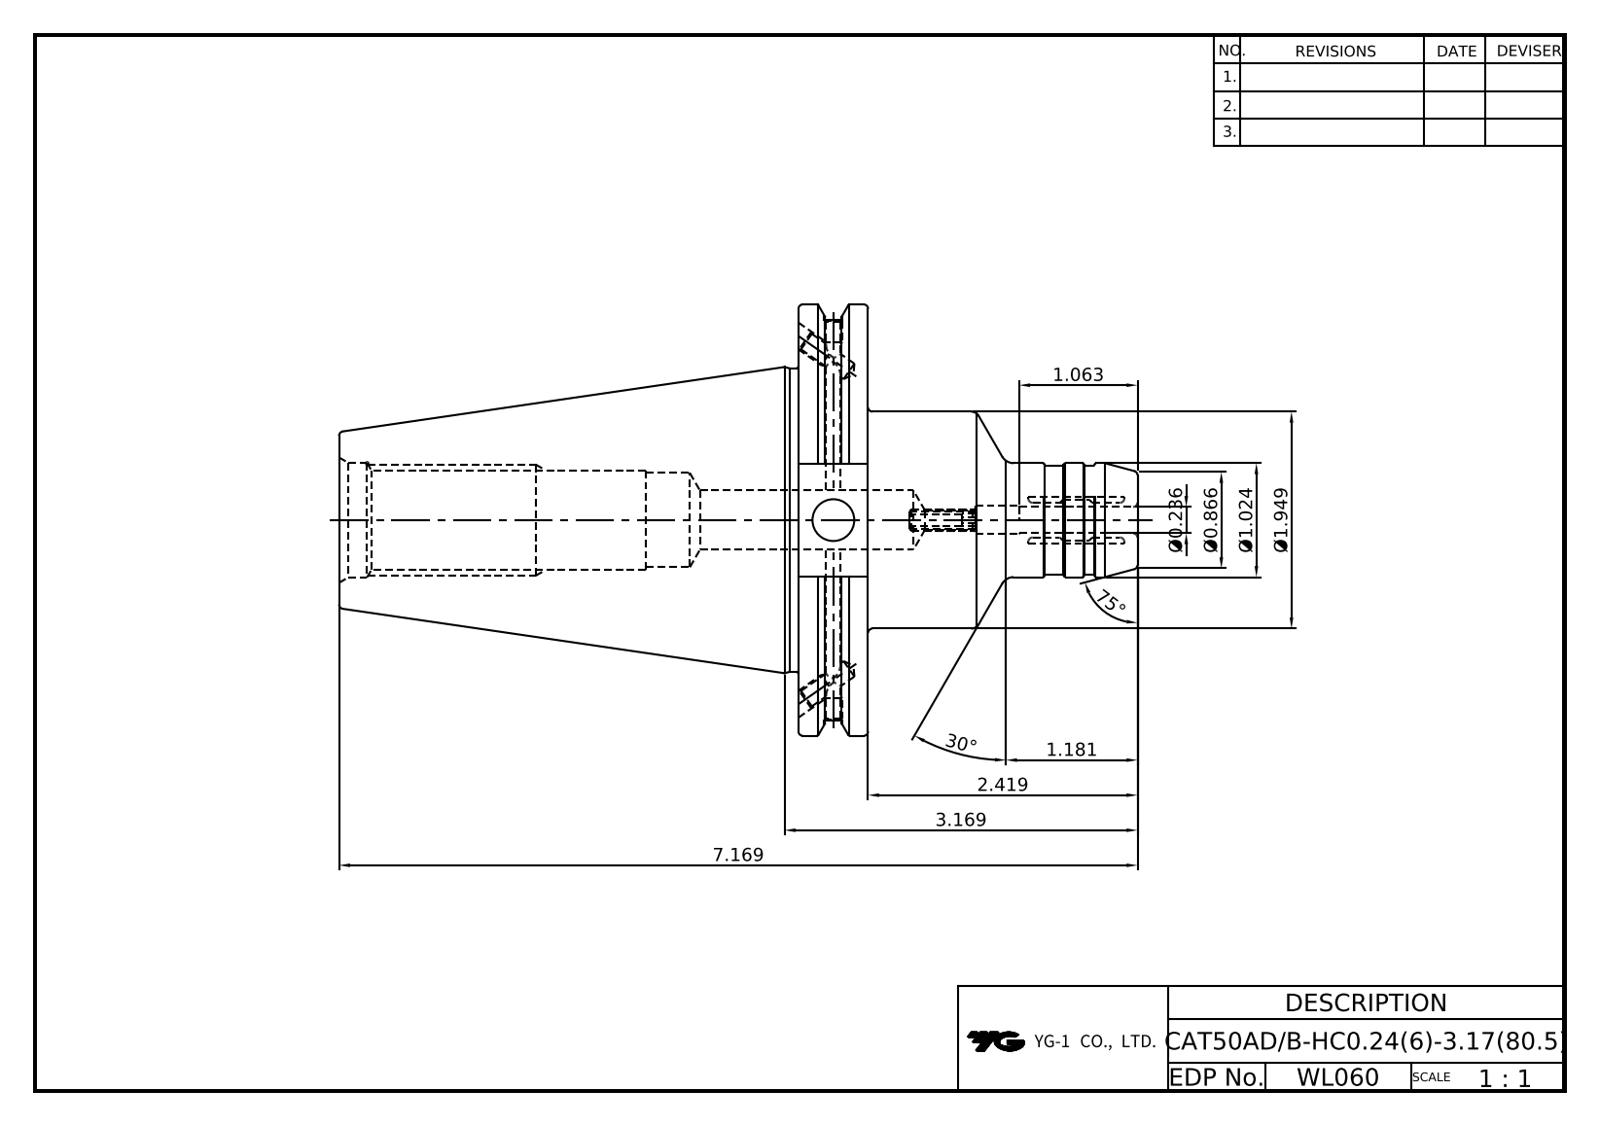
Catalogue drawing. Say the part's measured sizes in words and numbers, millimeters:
The part is named "LO-CAT50ADB-HC6-80.5". Its 3-D file was written by "Autodesk Inventor 2022 (AUTOMOTIVE_DESIGN)". It is 1 solid with 108 faces: 37 planar, 33 cylindrical and 38 other. Overall it measures 182.1 by 98.42 by 94.69 millimeters. Its volume is 395 201 cubic millimeters and its surface area 51 850 square millimeters. Round holes: 2 of diameter 3.24, 2 of diameter 4.13, 2 of diameter 4.2, 2 of diameter 5, 1 of diameter 4.3, 1 of diameter 6, 1 of diameter 6.6, 1 of diameter 9.53, 1 of diameter 13.5, 1 of diameter 20.5, 1 of diameter 21.97, 1 of diameter 26.2. Round bosses or shafts: 1 of diameter 98.42, 1 of diameter 91.29, 1 of diameter 69.25, 1 of diameter 49.5, 1 of diameter 26, 1 of diameter 25. The main face-to-face distances are 15.88, 104.77, 120.65, 73.03, 182.1, 77.33, 61.45, 25.9, 110.82, 6.05.
